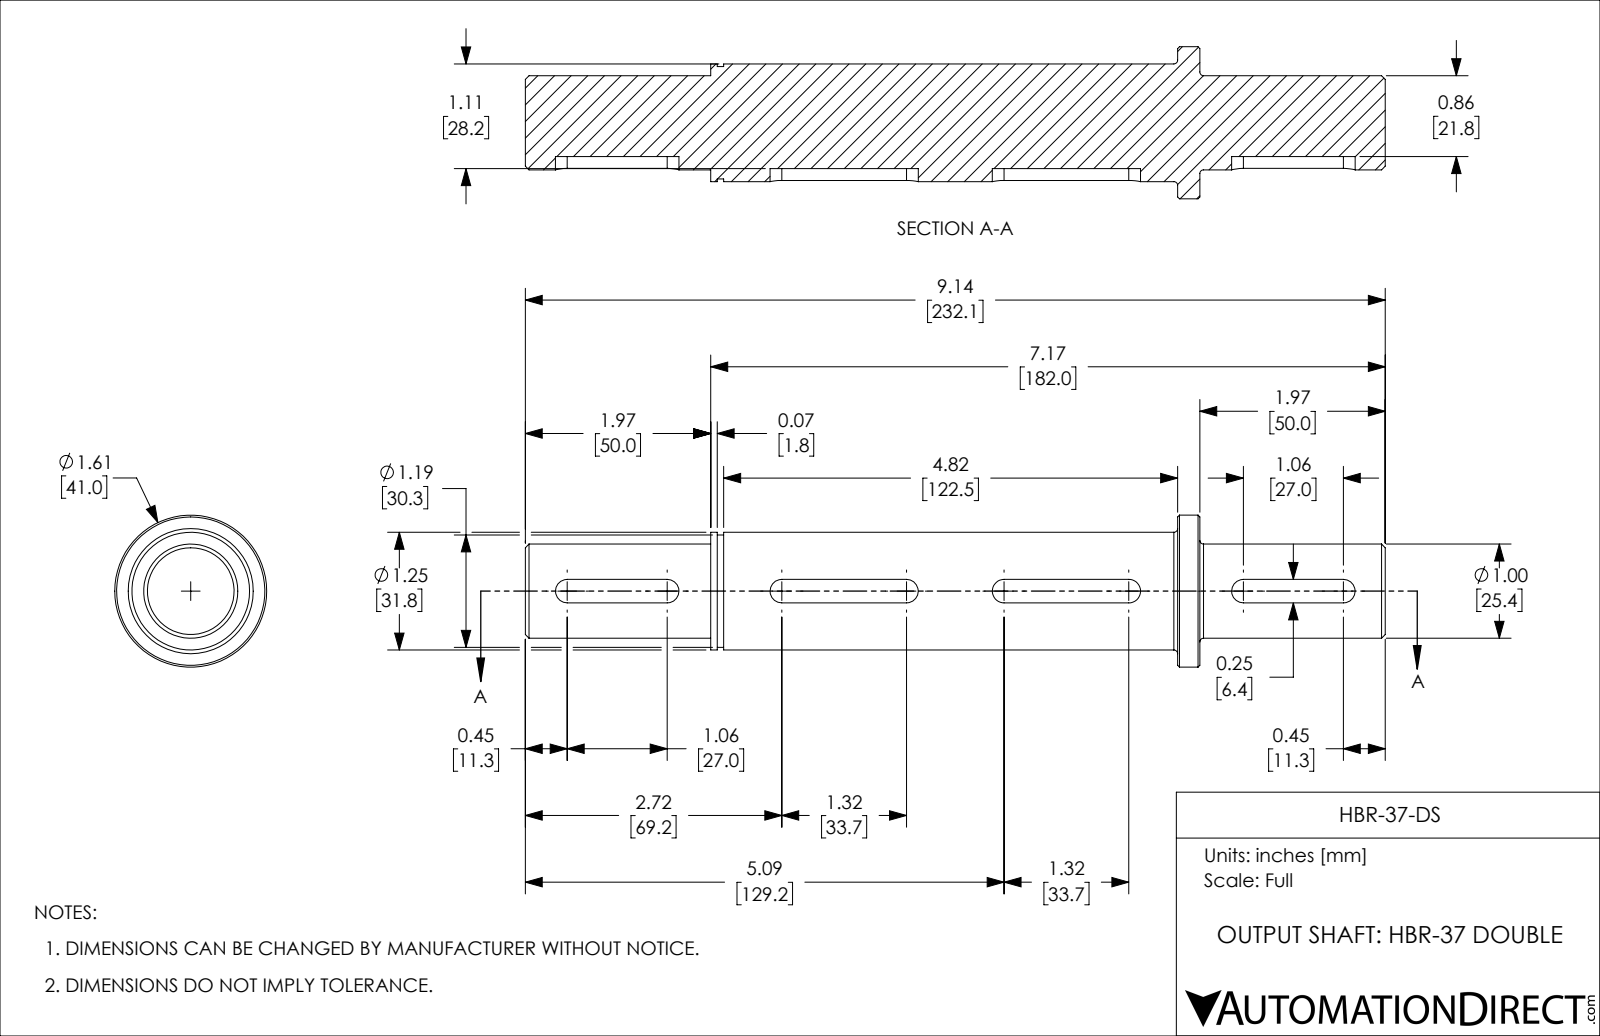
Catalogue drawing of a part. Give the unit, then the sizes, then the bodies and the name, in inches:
Units: inches
Overall size (bounding box): 9.137 × 1.614 × 1.614
Round bosses / shafts (diameter × count): ⌀1.614 ×1, ⌀1.25 ×1, ⌀1.193 ×1, ⌀1 ×1
Partial cylindrical surfaces — rounded edges, fillets, slot ends (radius × count): R0.125 ×8
Main face-to-face distances: 1.97, 7.167, 9.137, 0.128, 6.931, 0.236, 2.206, 0.25, 4.961, 5.197
Volume: 9.465 in³ · Surface area: 38.57 in²
Bodies: 1 solid, 55 faces (19 planar, 24 cylindrical, 12 other)
Part name (STEP PRODUCT): HBR-37-DS
STEP written by: SolidWorks 2018 (AUTOMOTIVE_DESIGN)
